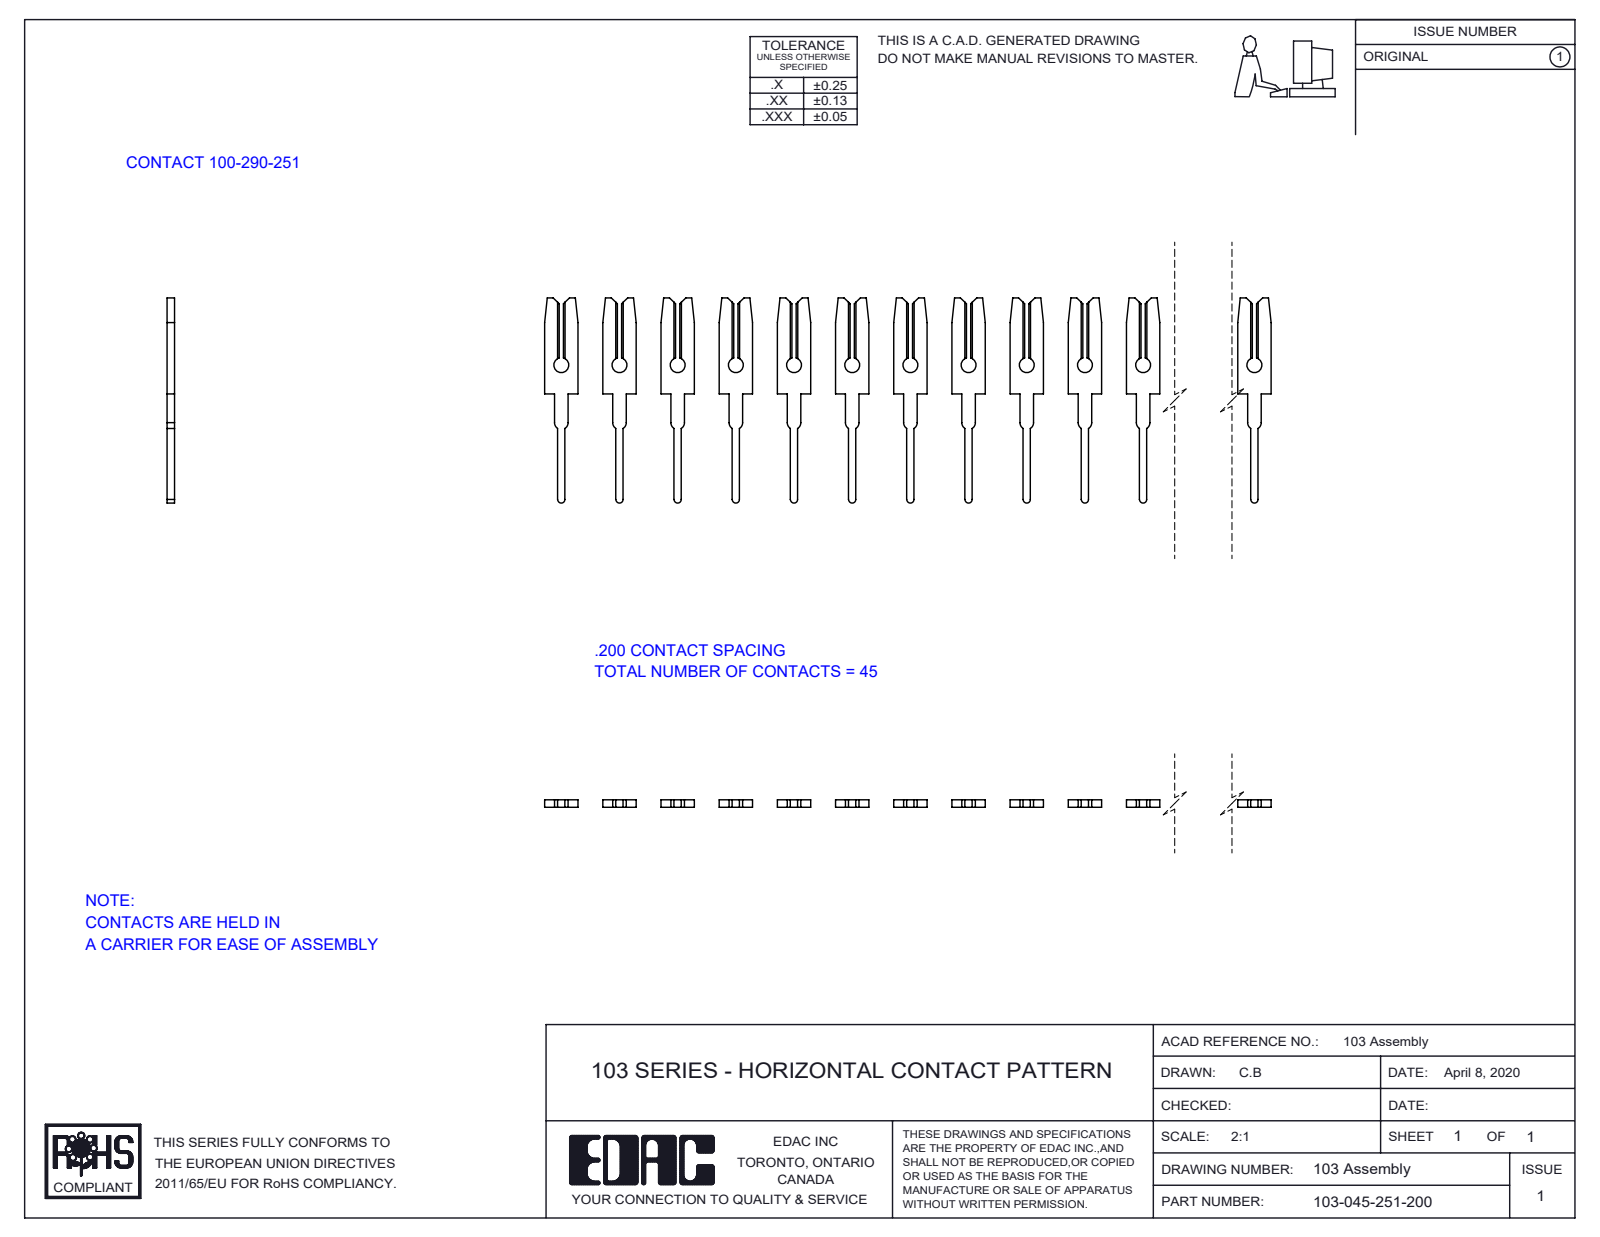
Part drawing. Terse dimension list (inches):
name: 100-290-001_100-290-251; 103-045-251-200
written by: SolidWorks 2016 (CONFIG_CONTROL_DESIGN)
unit: in
bodies: 45 solids, 1260 faces (990 planar, 270 cylindrical, 0 other)
size: 8.915 × 0.705 × 0.026
volume: 0.05 in³; area: 6.268 in²
holes: 45× ⌀0.052
rounds: 45× R0.012, 45× R0.024
face distances: 0.026, 0.141, 0.2, 0.4, 0.283, 0.848, 0.6, 0.99, 0.707, 0.8
hole spacings: 0.2, 0.4, 0.6, 0.8, 1, 1.2, 1.4, 1.6
